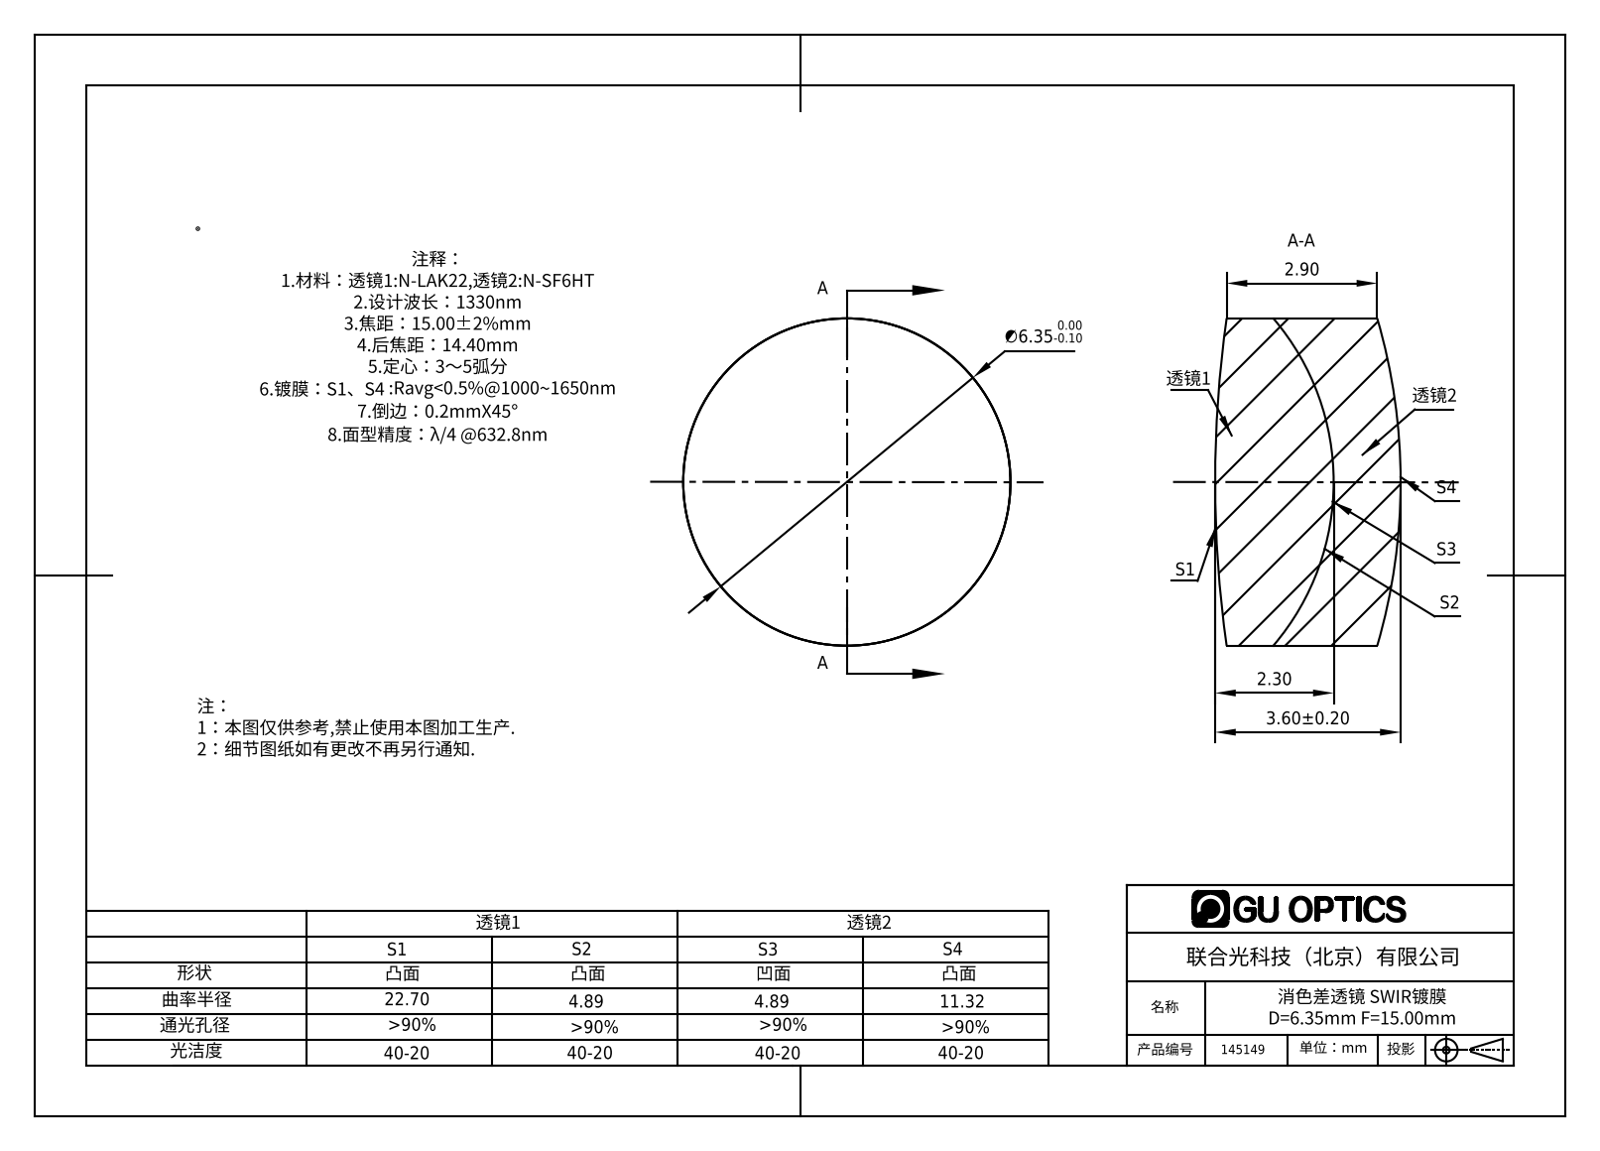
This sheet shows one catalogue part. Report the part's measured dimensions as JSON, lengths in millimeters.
{"part_name": "145149", "step_written_by": "SolidWorks 2016 (AUTOMOTIVE_DESIGN)", "units": "millimeters", "bodies": {"solids": 2, "faces": 12, "planar": 0, "cylindrical": 4, "other": 8}, "overall_size": [6.35, 6.35, 3.6], "volume_mm3": 103, "surface_area_mm2": 194, "round_bosses_or_shafts": [[6.35, 1]]}
